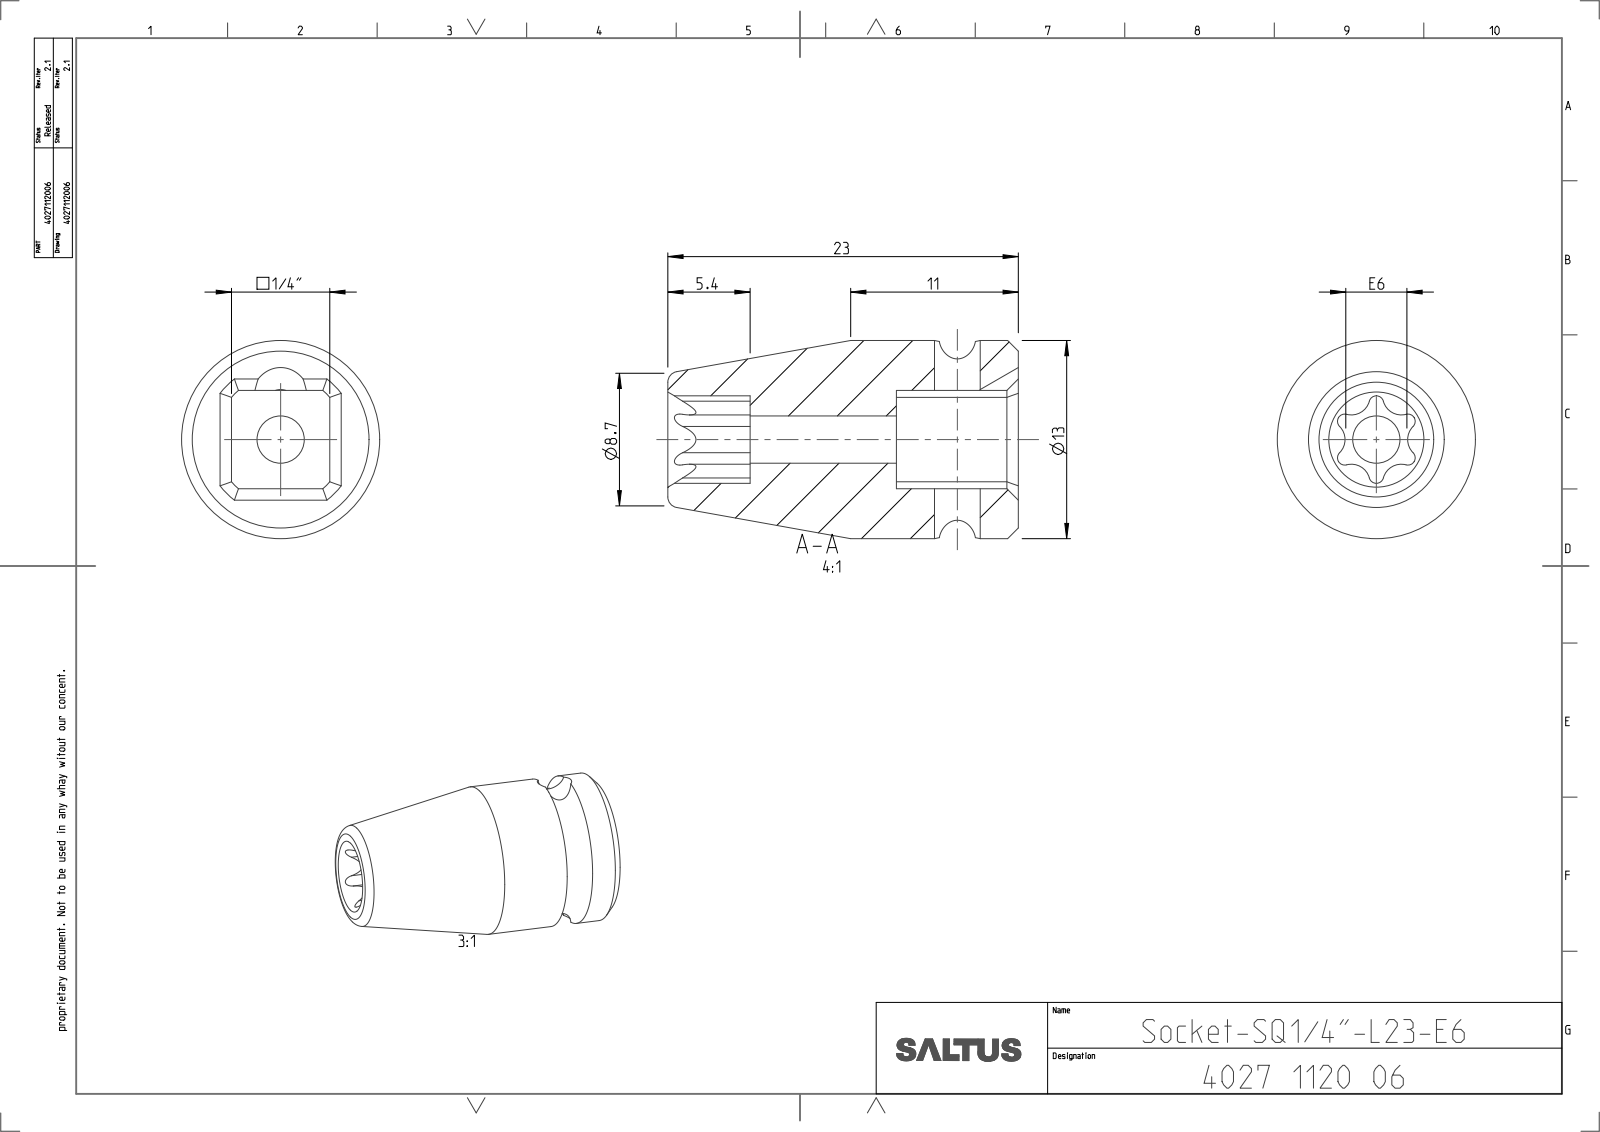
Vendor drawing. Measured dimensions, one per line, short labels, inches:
name: 4027112006
written by: CREO PARAMETRIC BY PTC INC, 2022414 (CONFIG_CONTROL_DESIGN)
unit: in
bodies: 1 solid, 54 faces (13 planar, 27 cylindrical, 14 other)
size: 0.906 × 0.512 × 0.512
volume: 0.119 in³; area: 2.23 in²
holes: 1× ⌀0.118, 1× ⌀0.122
bosses: 1× ⌀0.512
rounds: 6× R0.019, 6× R0.048, 1× R0.079, 1× R0.167
face distances: 0.254, 0.315, 0.906, 0.591, 0.693, 0.378, 0.213
